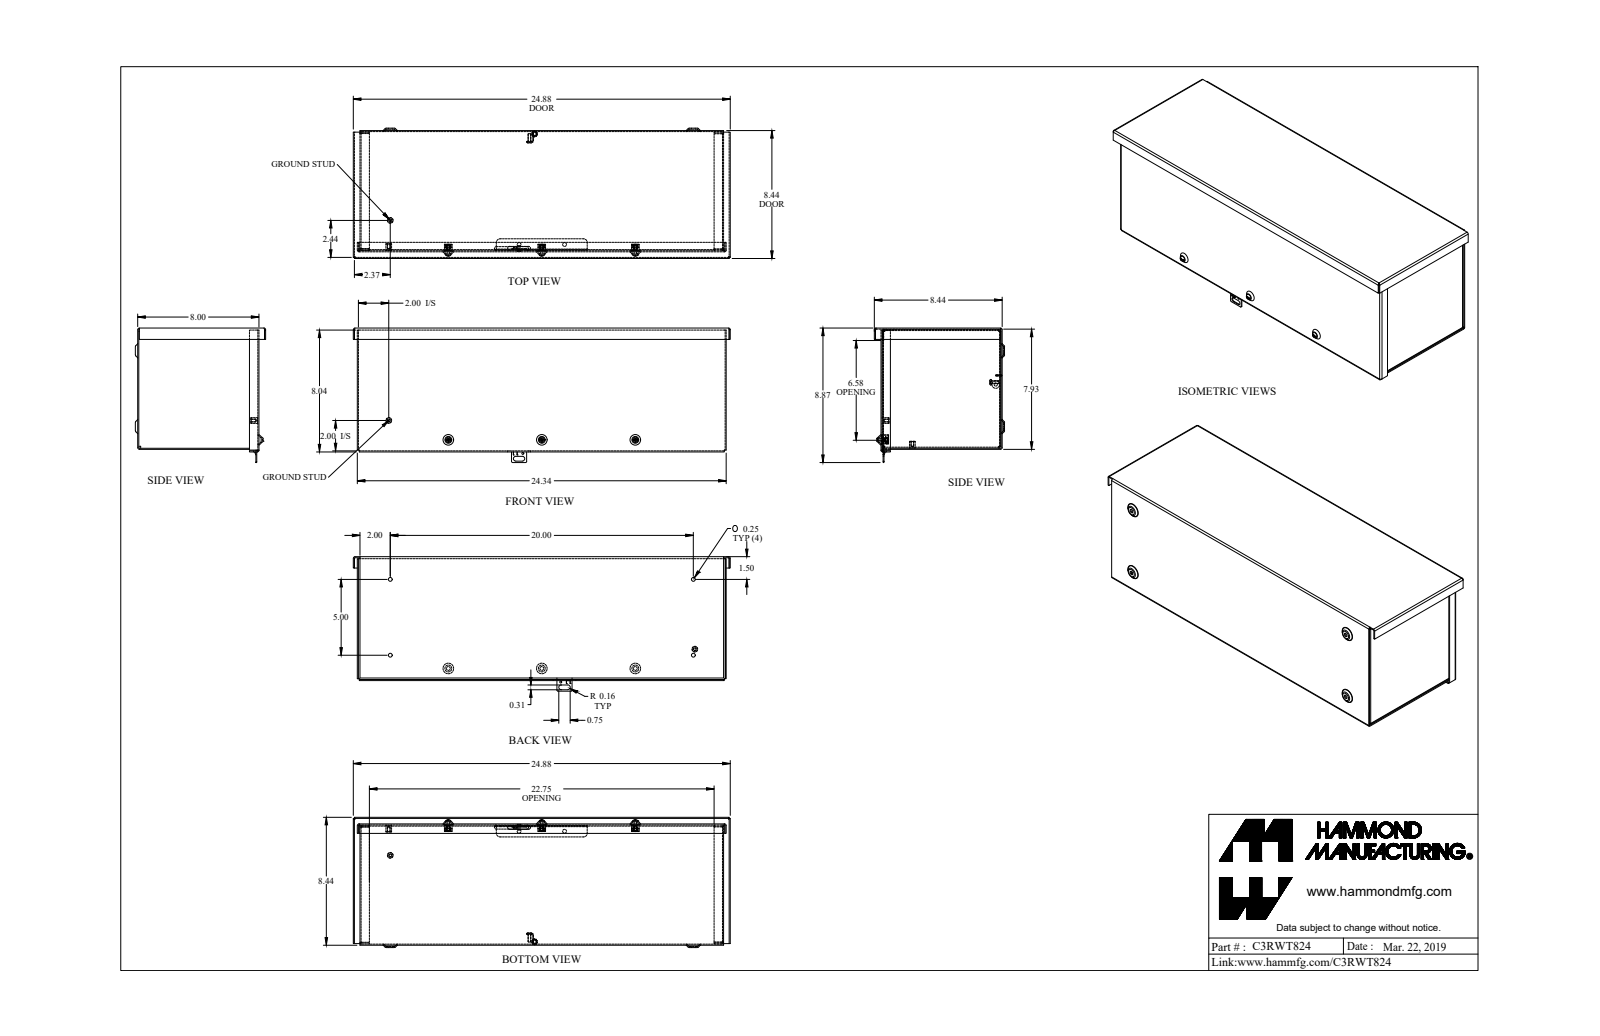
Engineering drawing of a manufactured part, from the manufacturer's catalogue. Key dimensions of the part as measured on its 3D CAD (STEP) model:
Part name (STEP PRODUCT): C3RWT824_Default
STEP written by: SolidWorks 2019 (CONFIG_CONTROL_DESIGN)
Units: inches
Bodies: 22 solids, 764 faces (415 planar, 237 cylindrical, 112 other)
Overall size (bounding box): 24.875 × 8.871 × 8.594
Volume: 73.32 in³ · Surface area: 2 062 in²
Round holes (diameter × count): ⌀0.25 ×6, ⌀0.156 ×5, ⌀0.214 ×3, ⌀0.23 ×3, ⌀0.203 ×2, ⌀0.125 ×1, ⌀0.137 ×1, ⌀0.2 ×1, ⌀0.215 ×1
Round bosses / shafts (diameter × count): ⌀0.19 ×4, ⌀0.148 ×3, ⌀0.375 ×2, ⌀0.5 ×1, ⌀0.367 ×1, ⌀0.21 ×1, ⌀0.152 ×1, ⌀0.125 ×1
Partial cylindrical surfaces — rounded edges, fillets, slot ends (radius × count): R0.036 ×18, R0.108 ×18, R0.08 ×12, R0.108 ×12, R0.125 ×11, R0.022 ×6, R0.25 ×6, R0.016 ×4
Main face-to-face distances: 0.072, 7.928, 7.856, 8, 23.928, 24, 23.856, 0.172, 0.144, 7.784
Hole centre spacings: 6.172, 3.927, 4.276, 7.352, 10.038, 11.598, 12.344, 13.144
